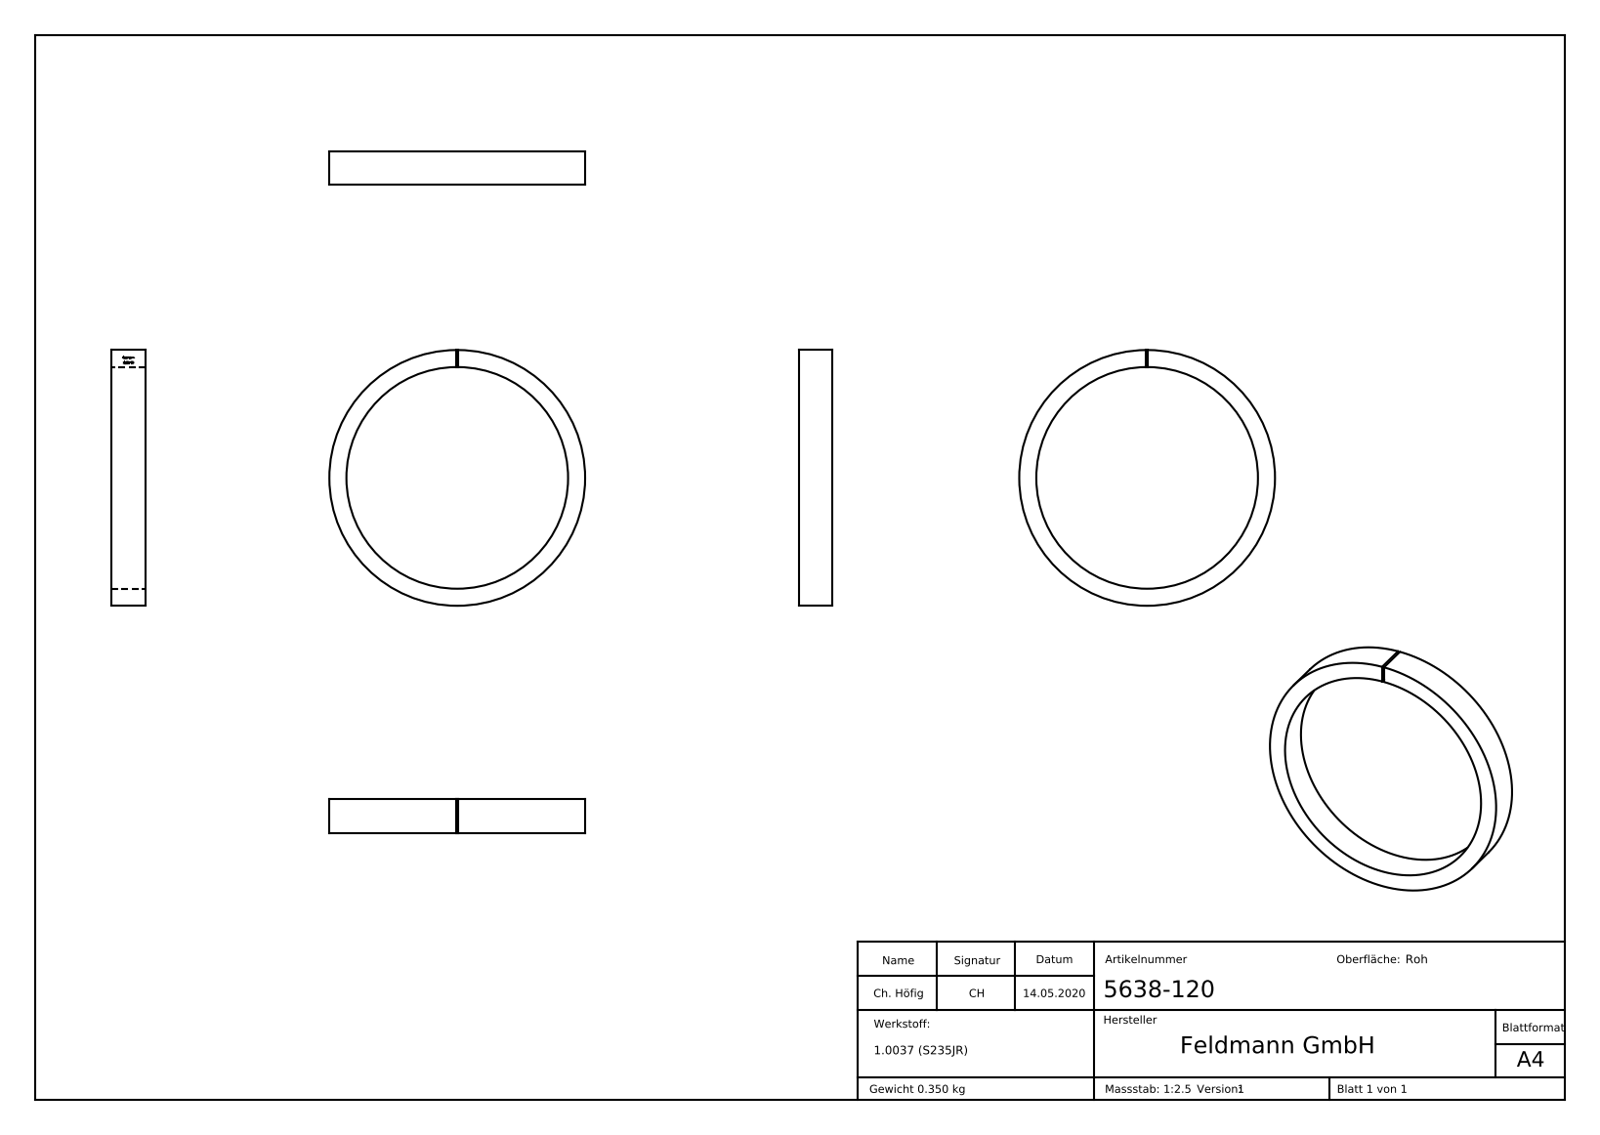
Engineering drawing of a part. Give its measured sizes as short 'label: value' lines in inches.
name: 5638-120
written by: SolidWorks 2015 (CONFIG_CONTROL_DESIGN)
unit: in
bodies: 1 solid, 222 faces (109 planar, 2 cylindrical, 111 other)
size: 4.724 × 4.724 × 0.63
volume: 2.741 in³; area: 26.51 in²
holes: 1× ⌀4.094
bosses: 1× ⌀4.724
face distances: 0.63, 0.039, 0.043, 0.07, 0.033, 0.083, 0.039, 0.109, 0.048, 0.131
